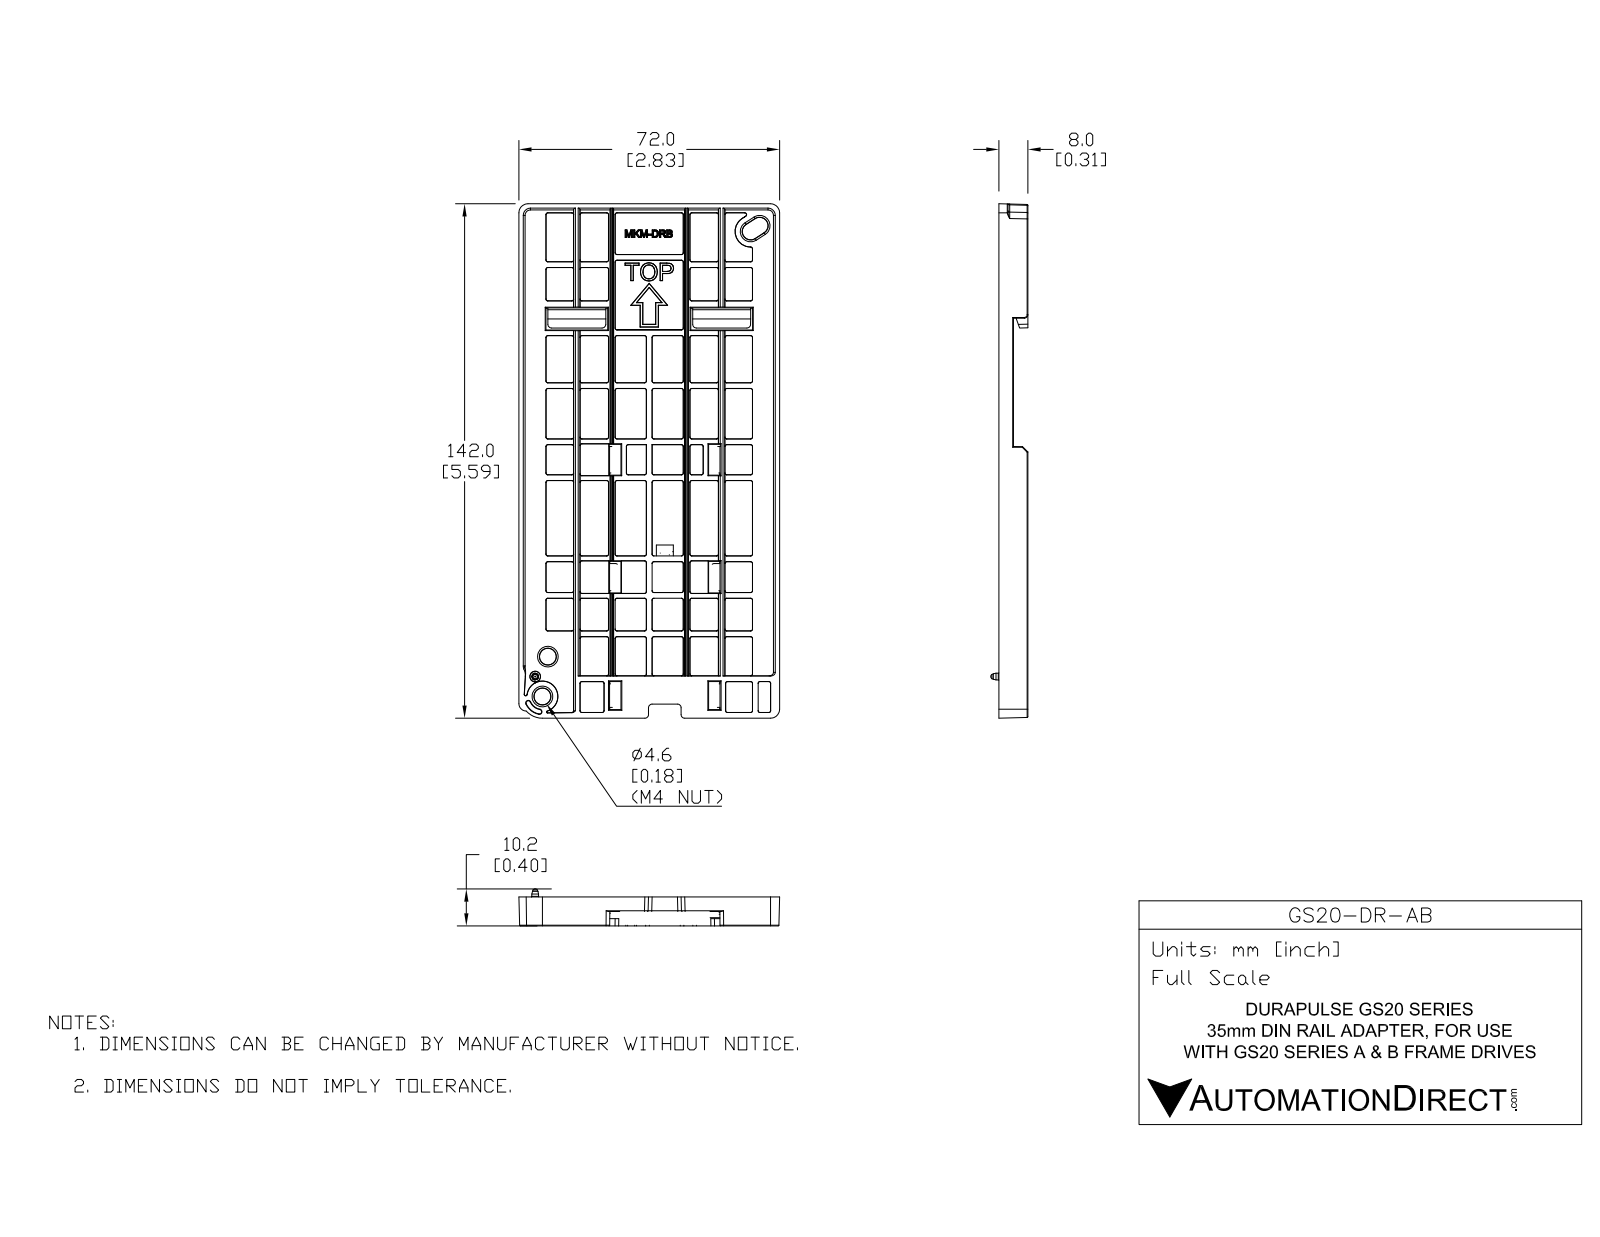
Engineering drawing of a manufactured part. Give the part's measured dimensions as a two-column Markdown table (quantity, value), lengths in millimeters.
| quantity | value |
| --- | --- |
| part name | MKM-DRB-PD-3D01 r1 |
| STEP written by | SolidWorks 2017 (AUTOMOTIVE_DESIGN) |
| units | millimeters |
| bodies | 10 solids, 2149 faces (928 planar, 821 cylindrical, 400 other) |
| overall size | 142 × 72 × 22.2 |
| volume | 42 380 mm³ |
| surface area | 40 170 mm² |
| round holes (diameter × count) | 4 × 3 |
| round bosses / shafts (diameter × count) | 8 × 4, 7 × 4, 4 × 1 |
| partial cylindrical surfaces (radius × count) | 0.5 × 364, 0.2 × 162, 1 × 96, 0.3 × 46, 1.5 × 6, 2 × 5, 0.8 × 4, 2.6 × 2 |
| main face-to-face distances | 2.5, 0.8, 3.3, 2, 4, 6.5, 0.7, 1.5, 7.3, 4.5 |
| hole center spacings | 3, 140.6, 143.1 |
